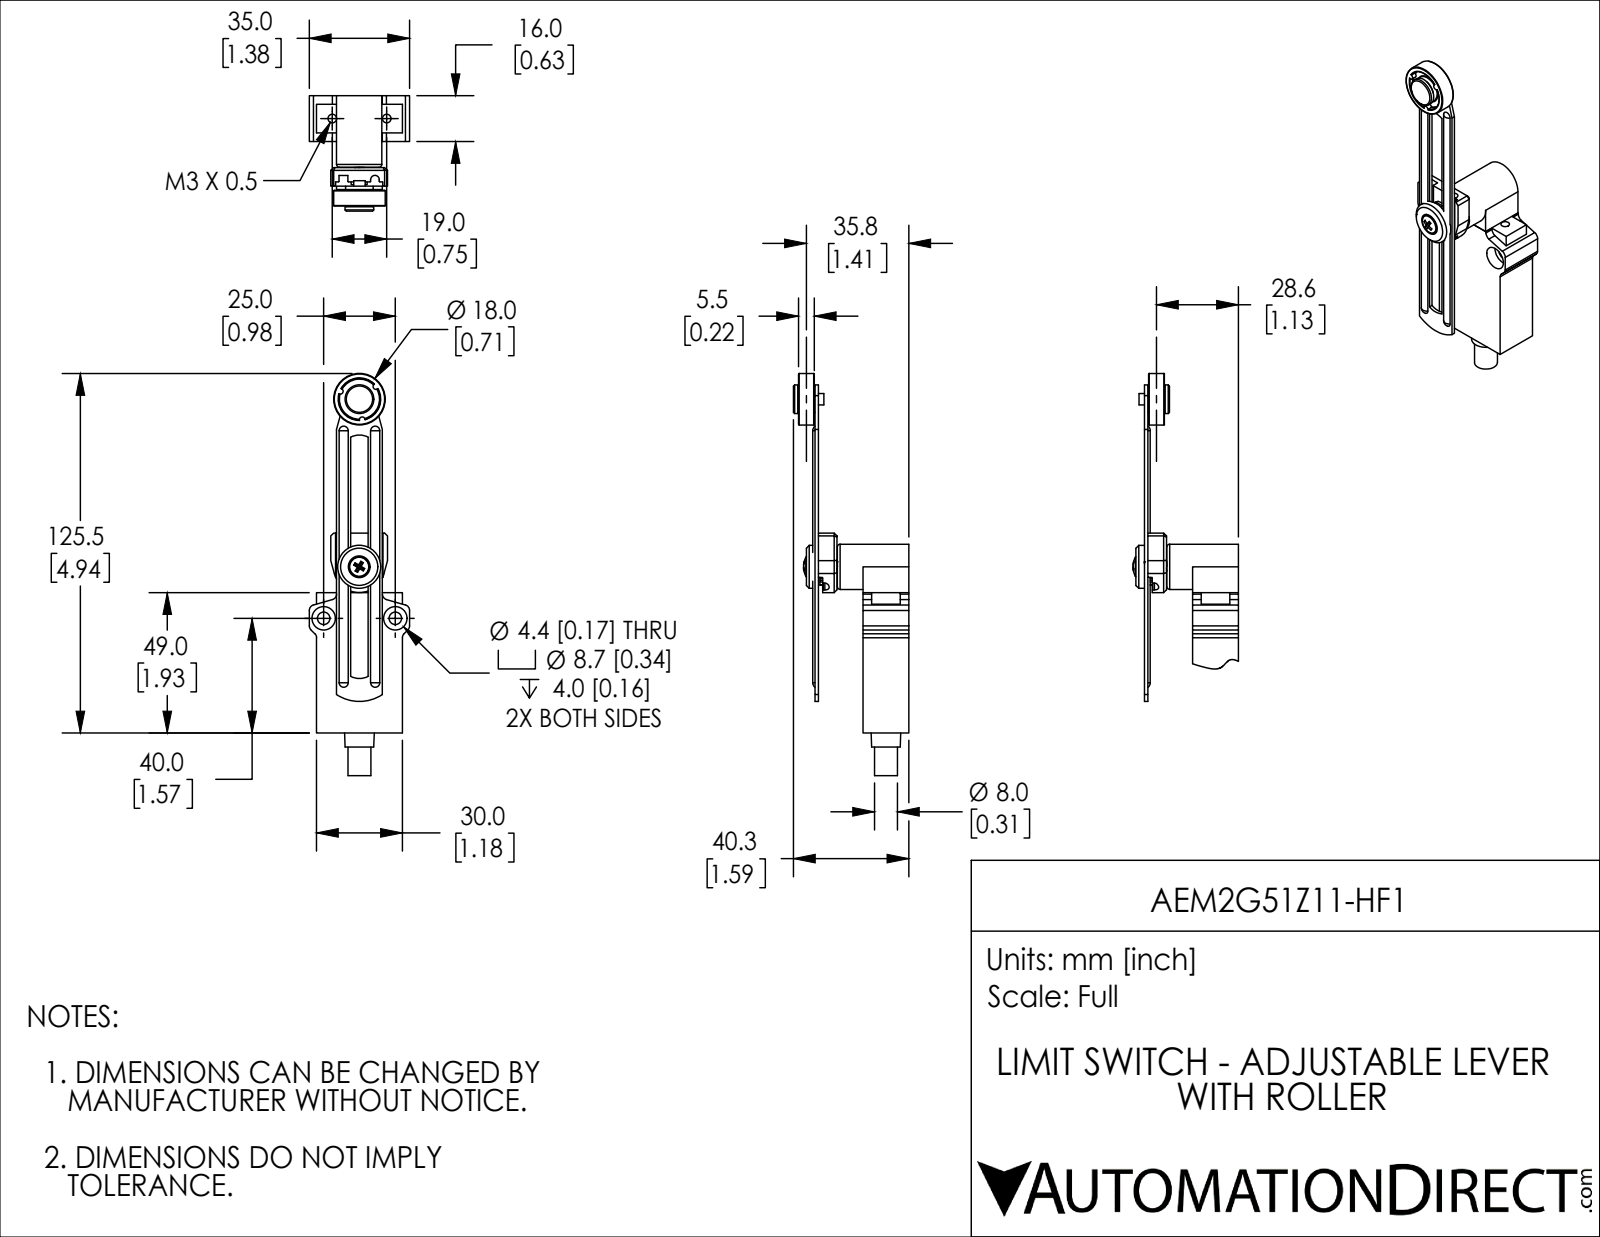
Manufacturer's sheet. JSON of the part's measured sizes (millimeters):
{"part_name": "AEM2G51Z11-HF1", "step_written_by": "SolidWorks 2018 (AUTOMOTIVE_DESIGN)", "units": "millimeters", "bodies": {"solids": 8, "faces": 486, "planar": 194, "cylindrical": 226, "other": 66}, "overall_size": [140.4, 40.3, 35], "volume_mm3": 33230, "surface_area_mm2": 15550, "round_holes": [[3, 2], [4.1, 2], [4.4, 2], [8.2, 2], [2.5, 1], [5, 1], [5.7, 1], [6.1, 1], [7.6, 1]], "round_bosses_or_shafts": [[18, 1], [15.8, 1], [15, 1], [10, 1], [8, 1], [7, 1], [6, 1], [4, 1]], "partial_cylinders_radius": [[0.2, 36], [2, 10], [0.2, 4], [1.2, 4], [1, 3], [6.5, 3], [0.8, 2], [1.5, 1]], "face_to_face_distances": [16, 32.8, 16.8, 1.2, 30, 15.6, 31.6, 49, 22.8, 7], "hole_center_spacings": [77.5, 19, 21.9, 22, 25, 58.5]}
